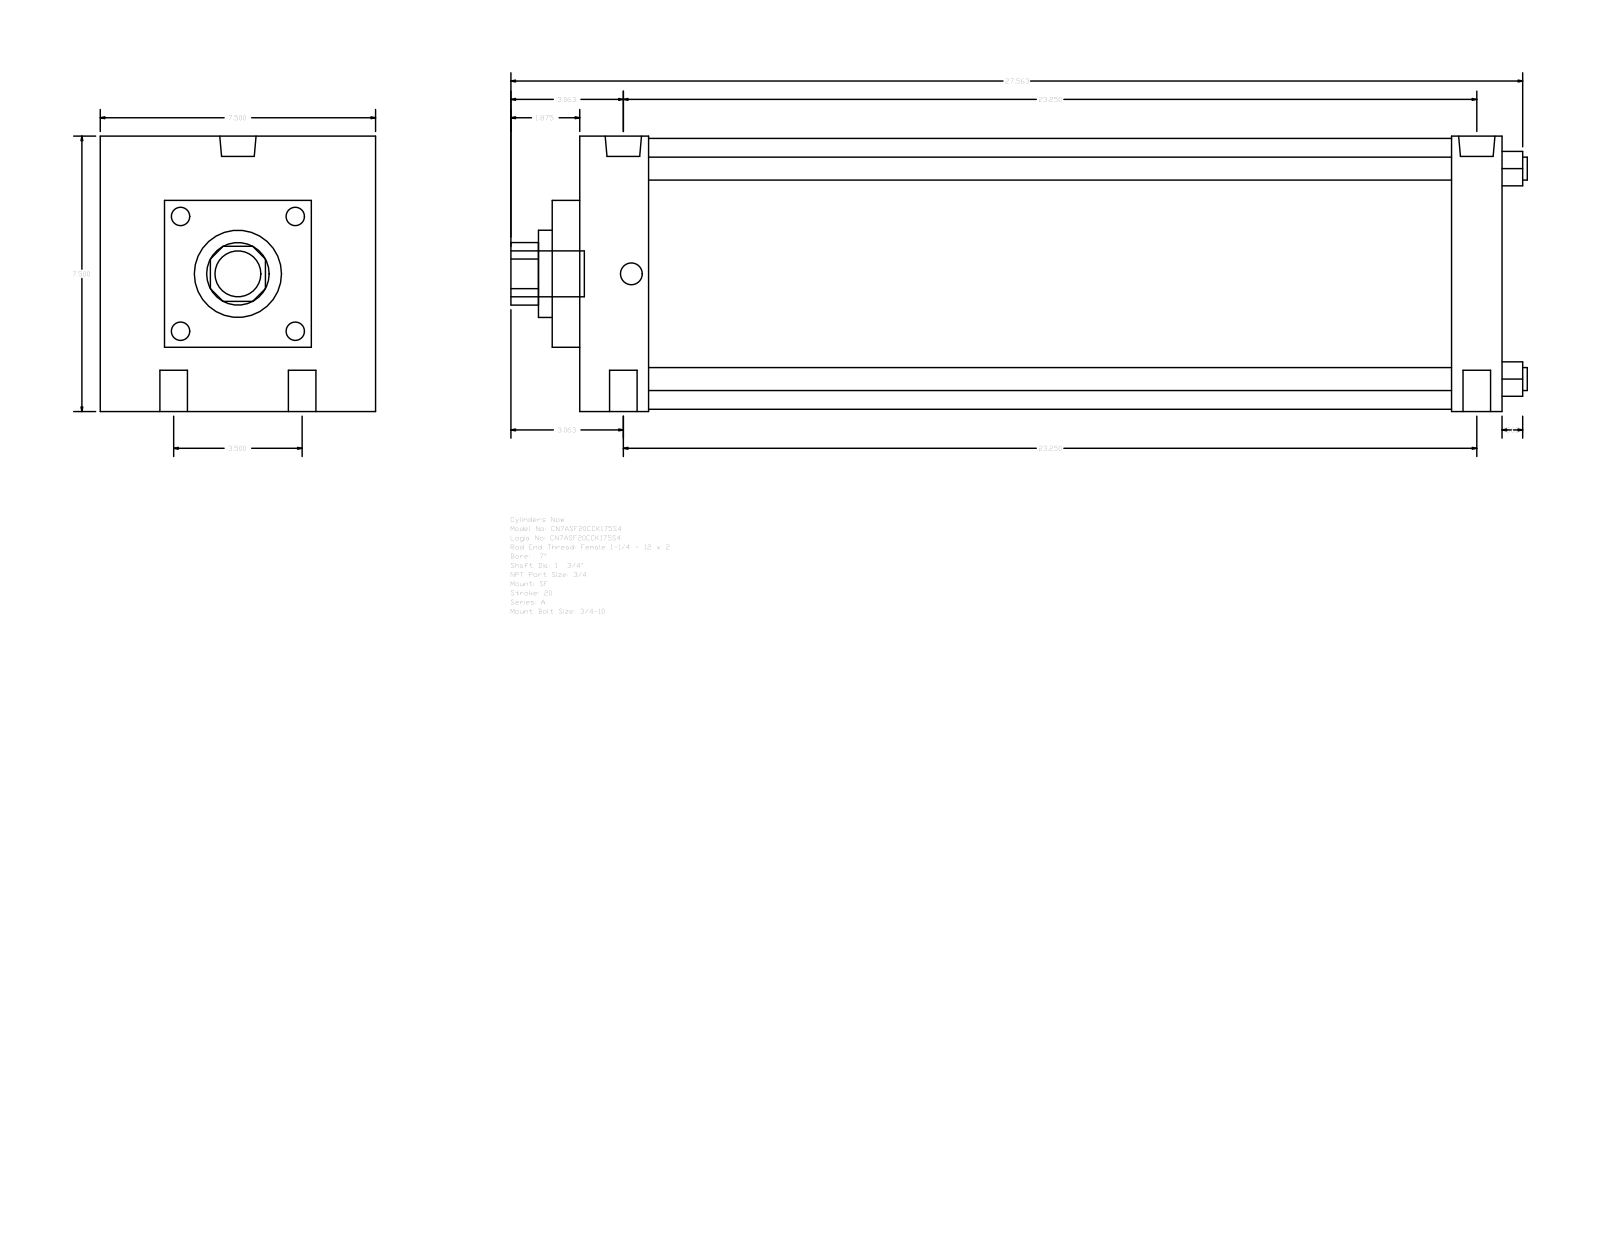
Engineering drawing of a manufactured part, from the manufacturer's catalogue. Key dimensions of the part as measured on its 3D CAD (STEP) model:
Part name (STEP PRODUCT): A_SF__0700_1.75
STEP written by: GSSL Pune (CONFIG_CONTROL_DESIGN)
Units: millimetres
Bodies: 0 solids, 93 faces (67 planar, 26 cylindrical, 0 other)
Overall size (bounding box): 703.26 × 190.5 × 190.5
Round holes (diameter × count): ⌀19.05 ×4, ⌀15.08 ×2, ⌀25.12 ×2, ⌀44.45 ×1, ⌀60.33 ×1
Round bosses / shafts (diameter × count): ⌀15.88 ×4, ⌀187.32 ×1, ⌀31.75 ×1
Partial cylindrical surfaces — rounded edges, fillets, slot ends (radius × count): R21.63 ×1
Main face-to-face distances: 190.5, 638.18, 44.45, 34.92, 19.05, 47.63, 603.26, 555.63, 590.55, 146.05
Hole centre spacings: 44.45, 592.22, 590.55, 88.9, 597.2, 579.43
